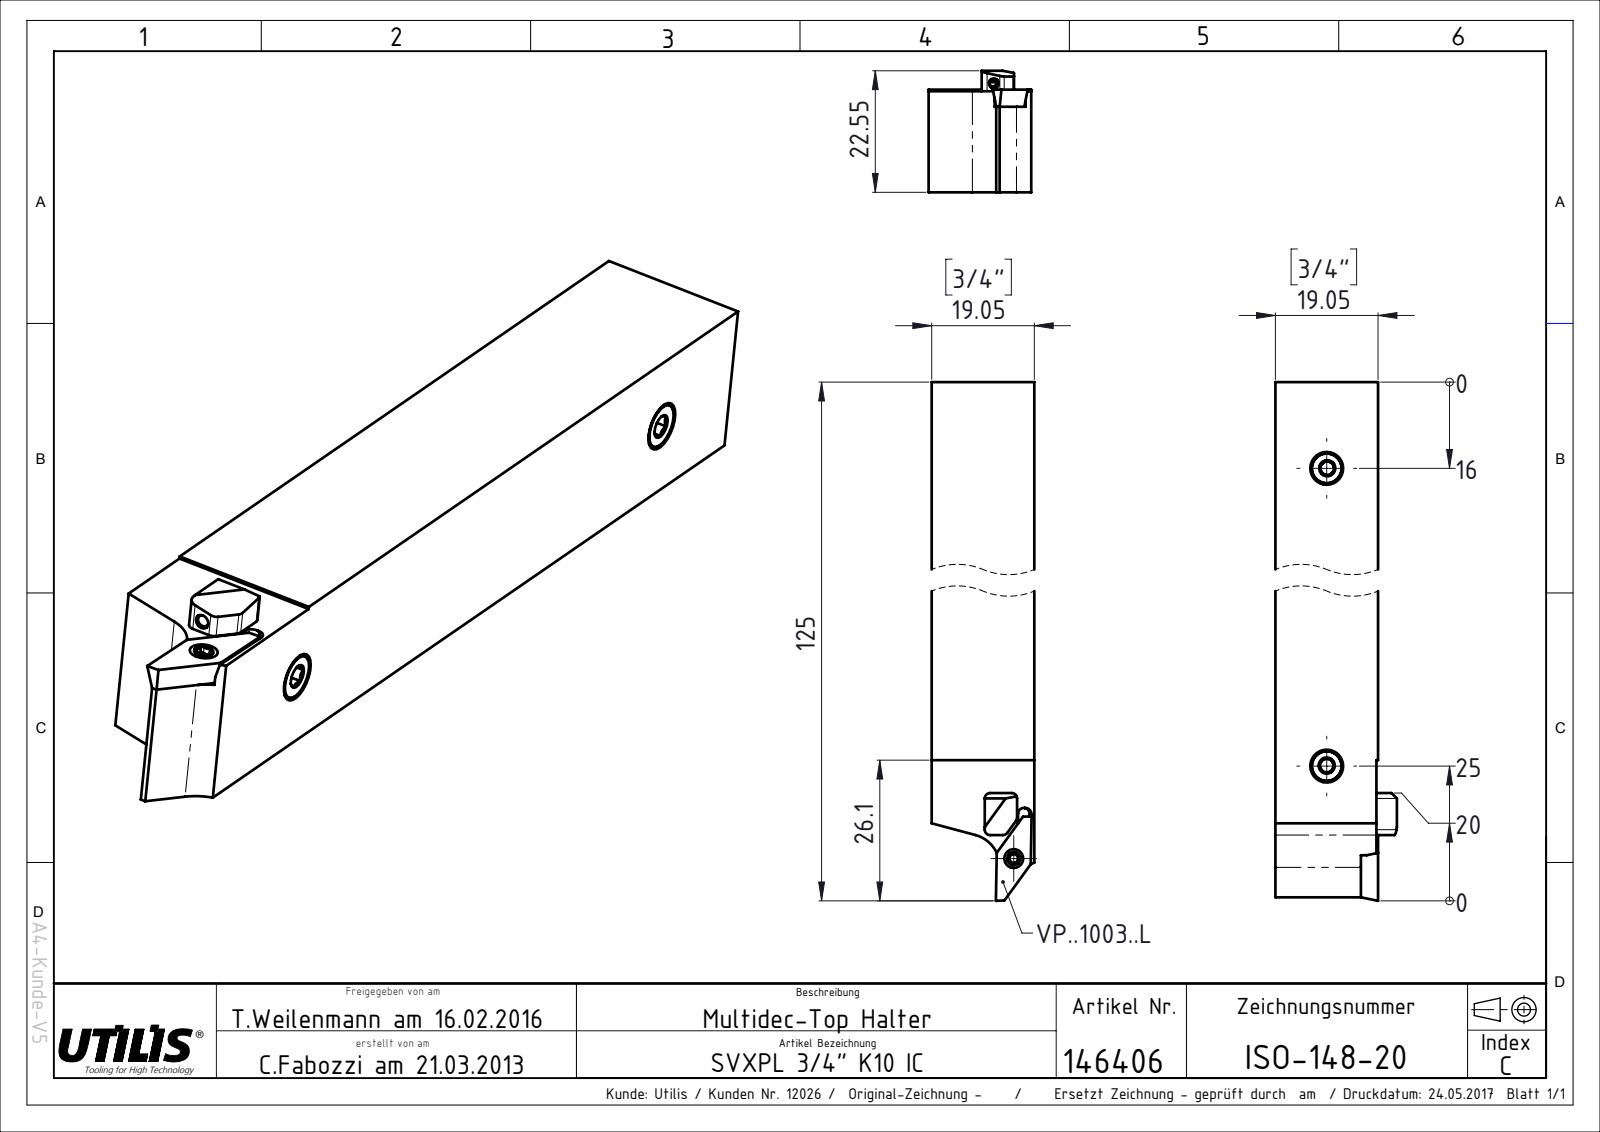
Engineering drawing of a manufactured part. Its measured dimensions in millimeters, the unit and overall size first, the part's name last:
Units: millimetres
Overall size (bounding box): 125 × 22.55 × 19.05
Partial cylindrical surfaces — rounded edges, fillets, slot ends (radius × count): R1 ×5, R6.1 ×2, R1.05 ×1
Main face-to-face distances: 19.05, 18.75, 9.85, 9.2, 105, 15.85, 6, 3.2, 5.33, 22.55
Volume: 41 958 mm³ · Surface area: 9 875 mm²
Bodies: 1 solid, 45 faces (35 planar, 9 cylindrical, 1 other)
Part name (STEP PRODUCT): ISO-148-20
STEP written by: SolidWorks 2016 (AUTOMOTIVE_DESIGN)
